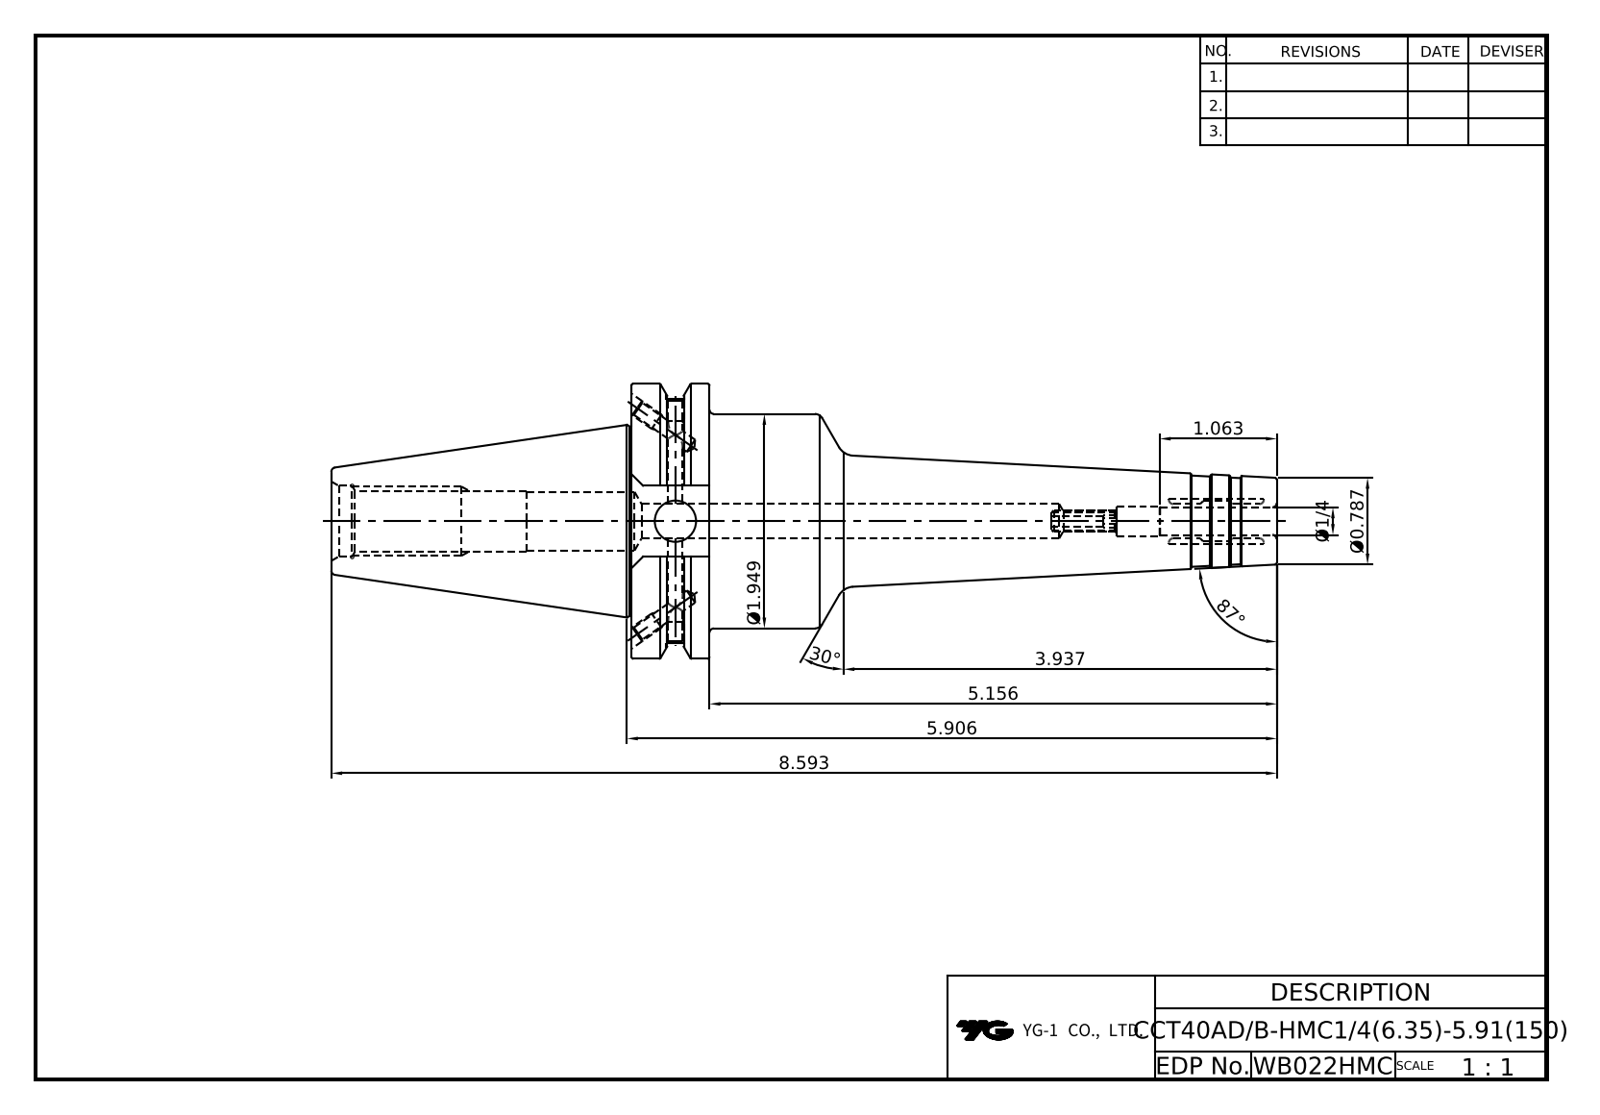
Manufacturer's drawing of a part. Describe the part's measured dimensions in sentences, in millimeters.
The part is named "LO-CCT40ADB-HMC6.35-150". Its 3-D file was written by "Autodesk Inventor 2025 (AUTOMOTIVE_DESIGN)". It is 1 solid with 107 faces: 36 planar, 30 cylindrical and 41 other. Overall it measures 218.25 by 63.5 by 61.09 millimeters. Its volume is 206 138 cubic millimeters and its surface area 35 410 square millimeters. Round holes: 4 of diameter 3.24, 2 of diameter 4, 2 of diameter 4.2, 1 of diameter 4.13, 1 of diameter 6.35, 1 of diameter 6.8, 1 of diameter 8, 1 of diameter 9.53, 1 of diameter 13, 1 of diameter 13.39, 1 of diameter 16.3. Round bosses or shafts: 1 of diameter 63.5, 1 of diameter 49.5. Partial cylindrical surfaces (rounded edges, fillets, slot ends): 1 of radius 8.19, 1 of radius 28.15. The main face-to-face distances are 18.05, 149, 130.95, 47.6, 16.38, 69.25, 87.3, 218.25, 81.3, 12.05.
